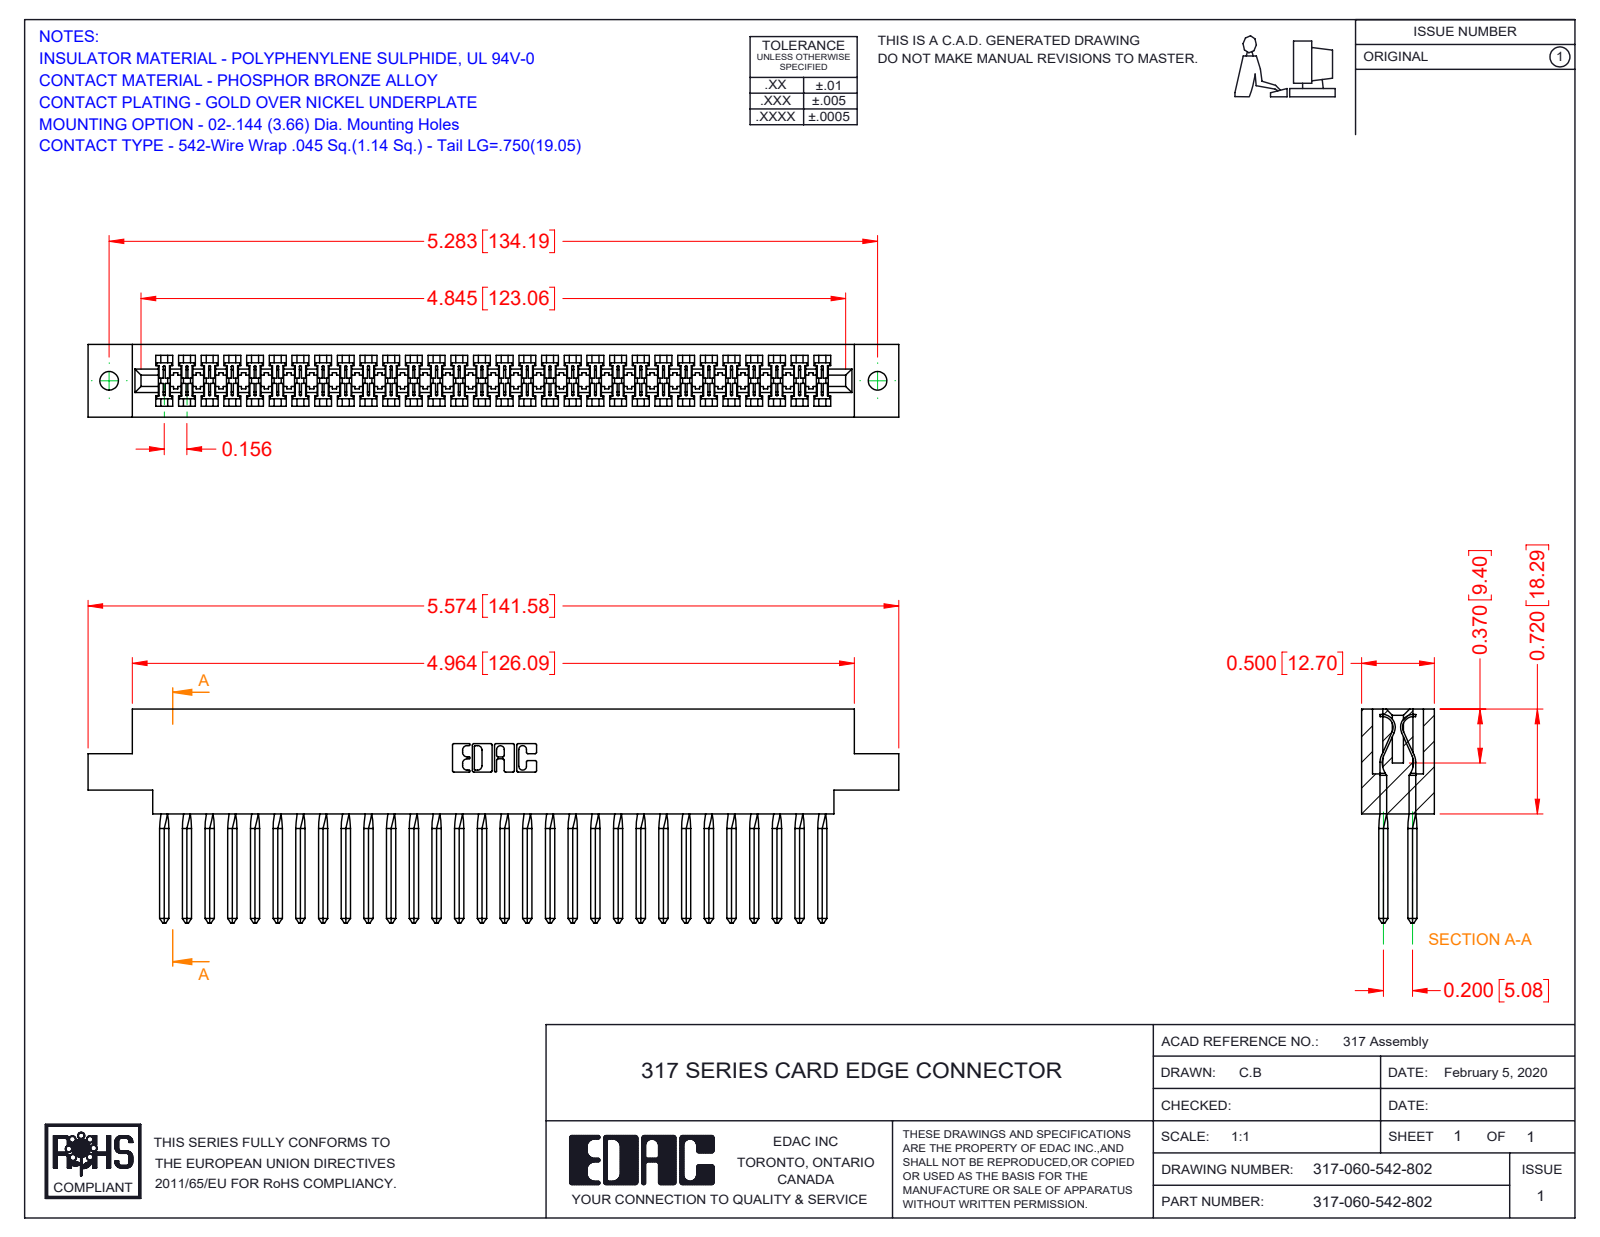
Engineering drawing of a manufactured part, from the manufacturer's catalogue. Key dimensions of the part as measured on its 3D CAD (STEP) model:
Part name (STEP PRODUCT): 317 Part_.144 Dia; 317-290-003_542; 317-060-542-802
STEP written by: SolidWorks 2016 (CONFIG_CONTROL_DESIGN)
Units: inches
Bodies: 61 solids, 3522 faces (2818 planar, 464 cylindrical, 240 other)
Overall size (bounding box): 5.574 × 1.47 × 0.5
Volume: 1.389 in³ · Surface area: 48.06 in²
Round holes (diameter × count): ⌀0.128 ×2
Partial cylindrical surfaces — rounded edges, fillets, slot ends (radius × count): R0.006 ×120, R0.01 ×22, R0.007 ×6, R0.031 ×6, R0.026 ×3, R0.074 ×2, R0.089 ×2, R0.1 ×2
Main face-to-face distances: 0.5, 0.075, 0.425, 0.35, 0.2, 0.11, 0.116, 0.046, 0.128, 0.372
Hole centre spacings: 5.283
